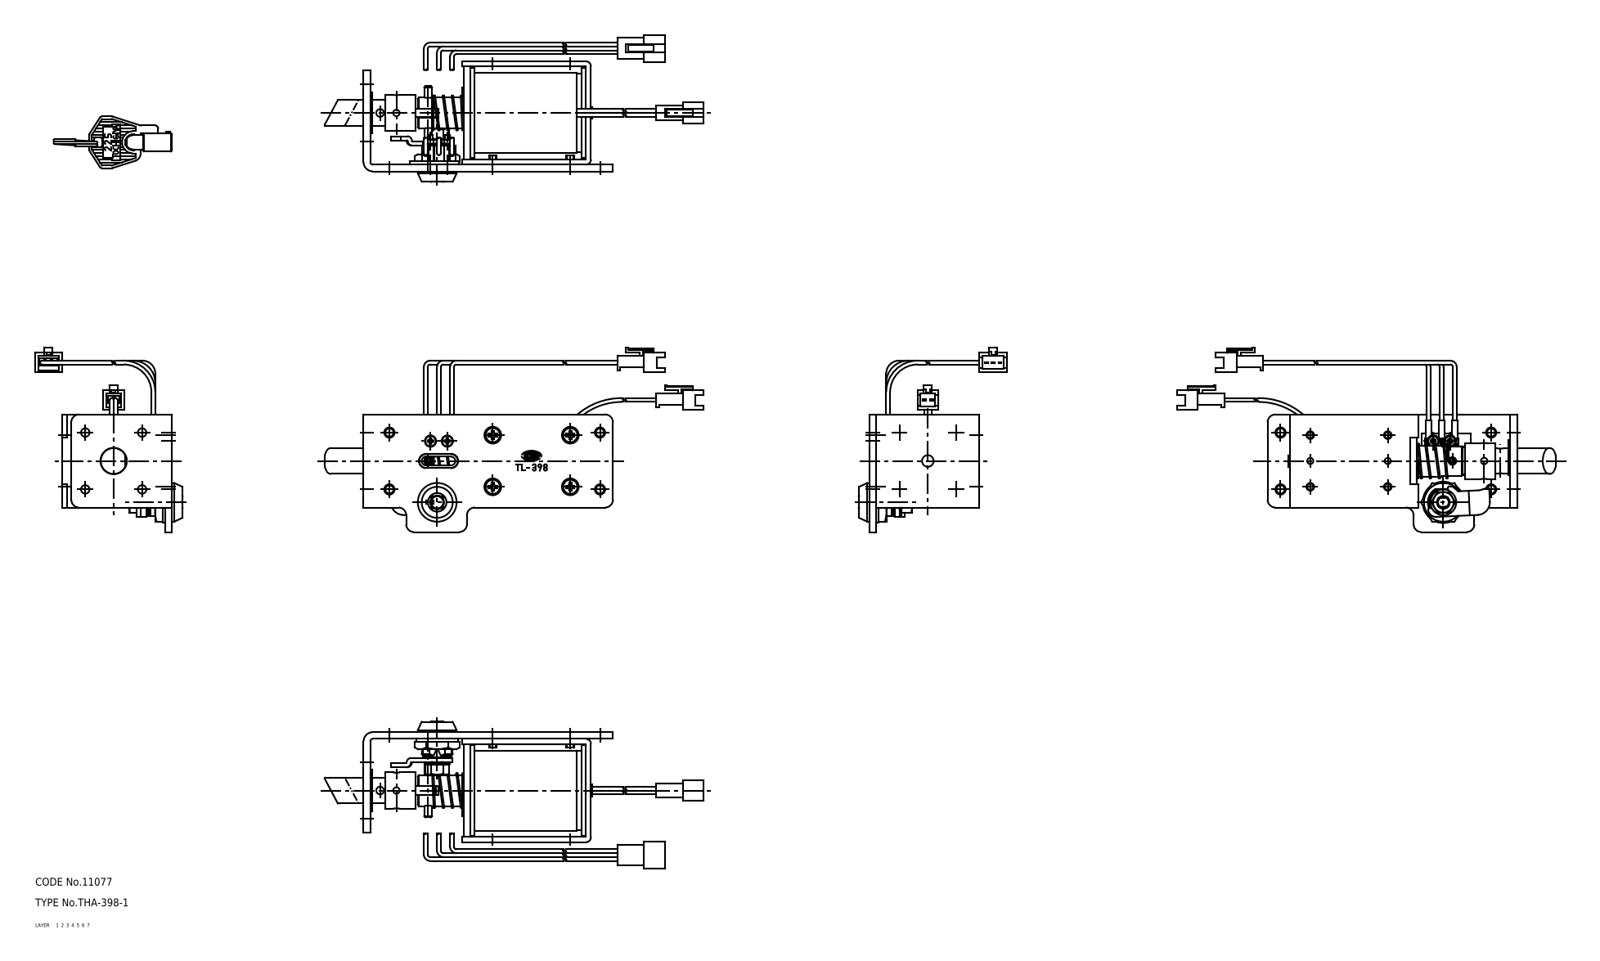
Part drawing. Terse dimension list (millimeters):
name: 67147565; 67147578; 67147591; 67147604 (+3 more)
written by: CADfix (AUTOMOTIVE_DESIGN)
unit: mm
bodies: 7 solids, 769 faces (0 planar, 0 cylindrical, 769 other)
size: 146.5 × 131.97 × 71.35
volume: 71 581 mm³; area: 38 654 mm²
